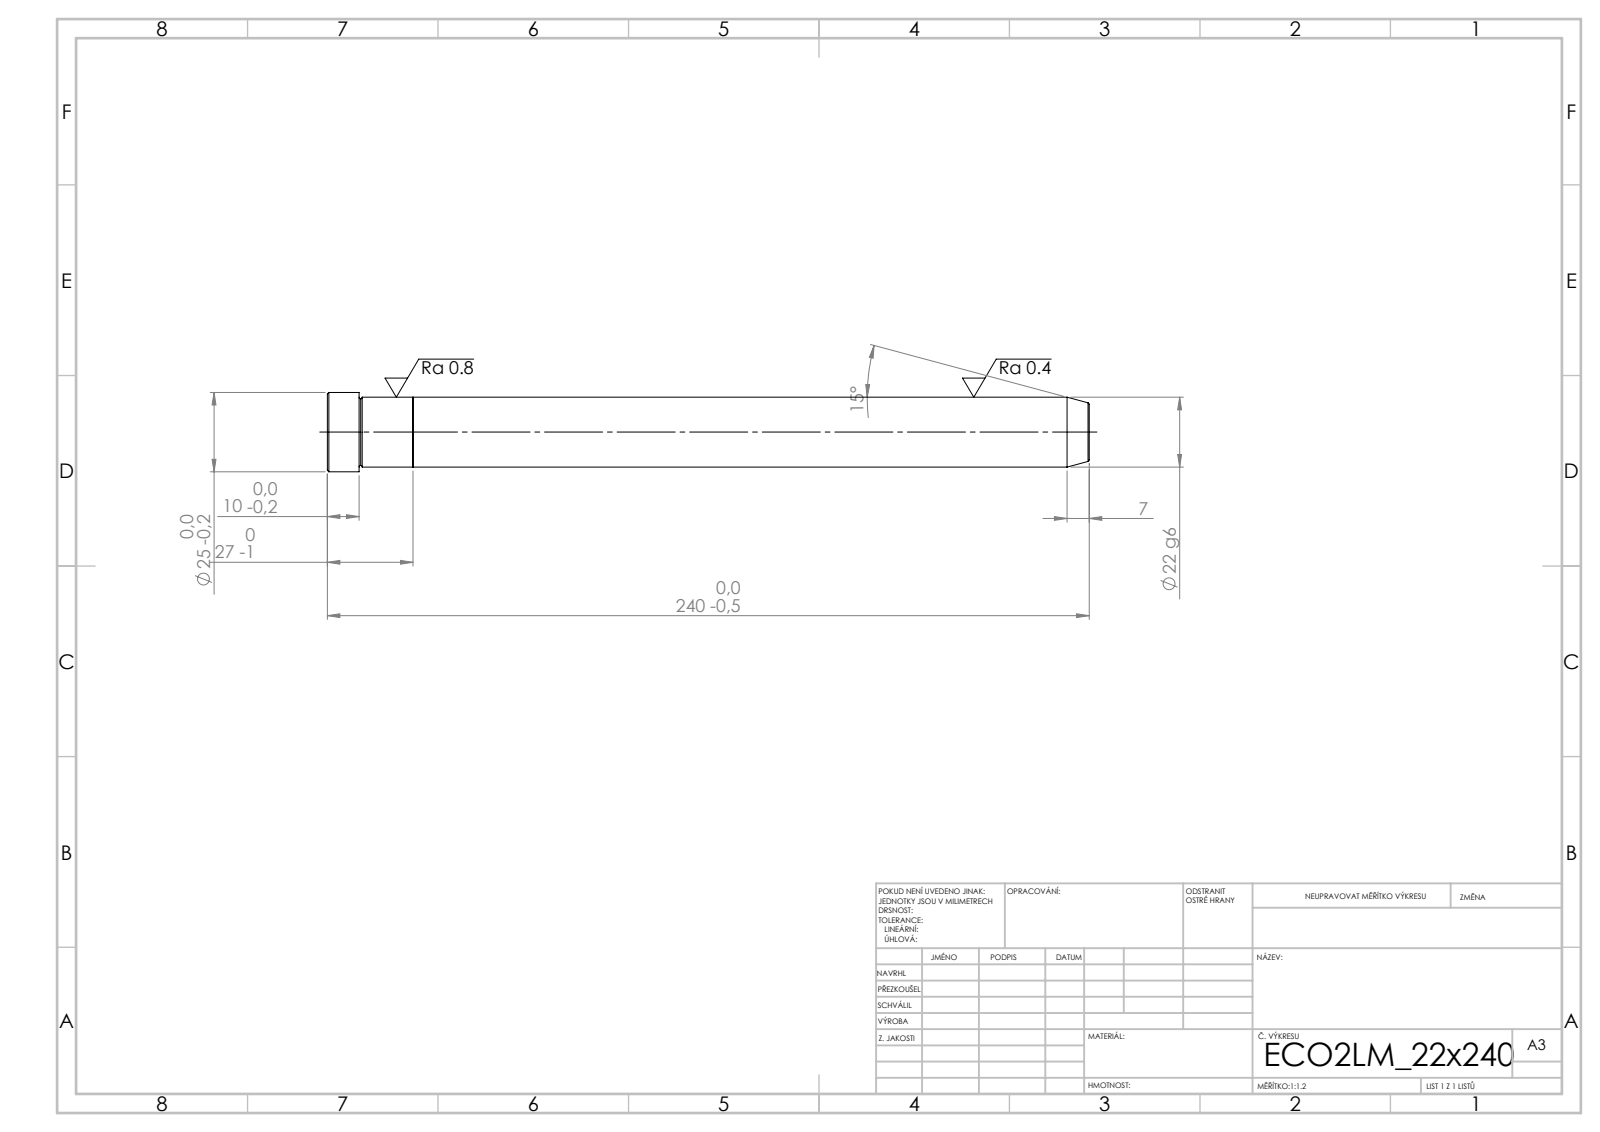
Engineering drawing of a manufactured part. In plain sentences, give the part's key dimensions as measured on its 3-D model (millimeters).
Its 3-D file was written by "SolidWorks 2019 (CONFIG_CONTROL_DESIGN)". It is 2 solids with 21 faces: 5 planar, 6 cylindrical and 10 other. Overall it measures 240 by 25 by 25 millimeters. Its volume is 91 873 cubic millimeters and its surface area 18 286 square millimeters. Round bosses or shafts: 1 of diameter 25, 1 of diameter 22. The main face-to-face distances are 27, 213, 240, 230, 17, 10.
